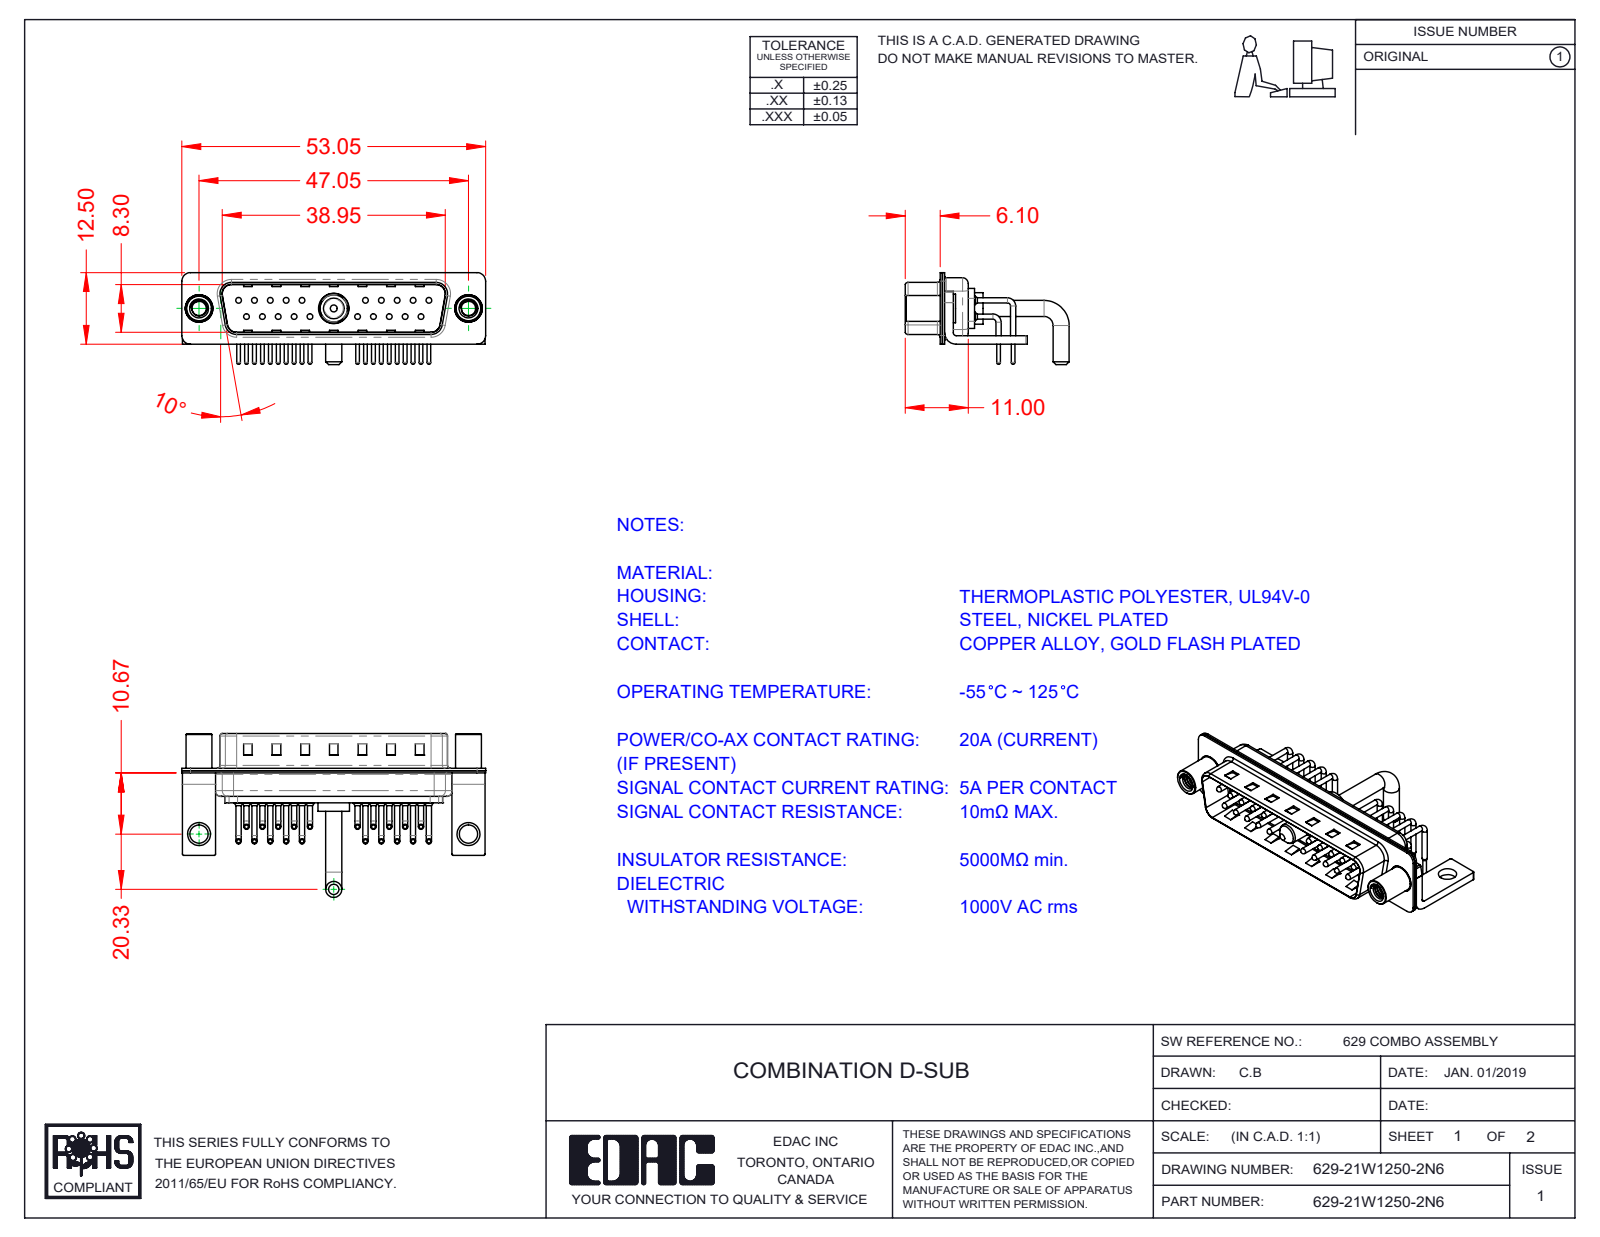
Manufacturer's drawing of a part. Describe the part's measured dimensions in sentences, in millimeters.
The part is named "629Combo Contact Row 1; 629Combo Stabilizer Bracket; 629Combo Housing_21W1; Power Pin_Ext 20A RA (+5 more)". Its 3-D file was written by "SolidWorks 2020 (CONFIG_CONTROL_DESIGN)". It is 29 solids with 2717 faces: 1483 planar, 950 cylindrical and 284 other. Overall it measures 53.05 by 28.63 by 16.05 millimeters. Its volume is 3 445 cubic millimeters and its surface area 8 583 square millimeters. Round holes: 20 of diameter 0.75, 20 of diameter 1.6, 20 of diameter 2, 2 of diameter 2.5, 2 of diameter 3.2, 2 of diameter 4, 2 of diameter 4.8, 1 of diameter 4.85, 1 of diameter 5.3. Round bosses or shafts: 40 of diameter 0.9, 20 of diameter 1.5, 20 of diameter 1, 20 of diameter 0.65, 2 of diameter 5, 2 of diameter 4.9, 2 of diameter 4.5, 2 of diameter 2.8. Partial cylindrical surfaces (rounded edges, fillets, slot ends): 20 of radius 1.01, 16 of radius 0.25, 16 of radius 1.5, 13 of radius 2, 9 of radius 0.5, 8 of radius 1.6, 4 of radius 0.6, 4 of radius 0.65. The main face-to-face distances are 0.4, 0.8, 9.5, 1.5, 9.1, 8.7, 9.9, 0.6, 2.1, 0.75. The hole center spacings are 3.16, 2.77, 5.54, 8.31, 5.04, 19.39, 20.97, 22.16.
